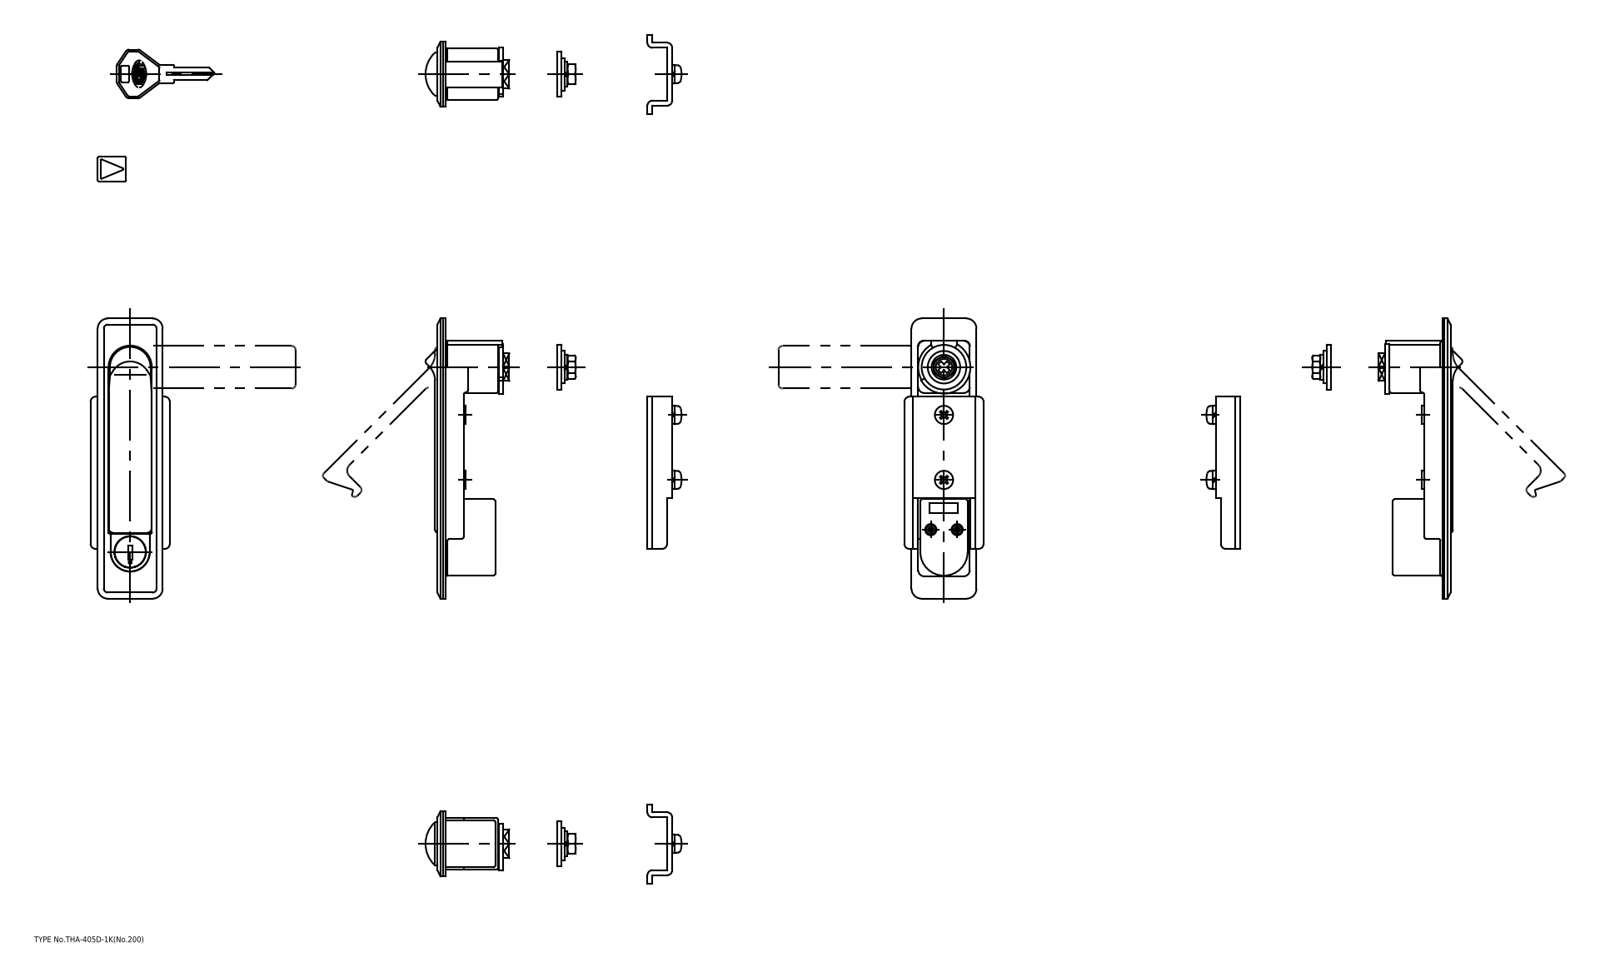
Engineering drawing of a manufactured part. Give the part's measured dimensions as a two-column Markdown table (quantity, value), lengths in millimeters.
| quantity | value |
| --- | --- |
| part name | screw; washer; shaft; packing (+8 more) |
| STEP written by | CADfix (AUTOMOTIVE_DESIGN) |
| units | millimeters |
| bodies | 12 solids, 526 faces (0 planar, 0 cylindrical, 526 other) |
| overall size | 138 × 121.83 × 39 |
| volume | 58 091 mm³ |
| surface area | 47 531 mm² |
